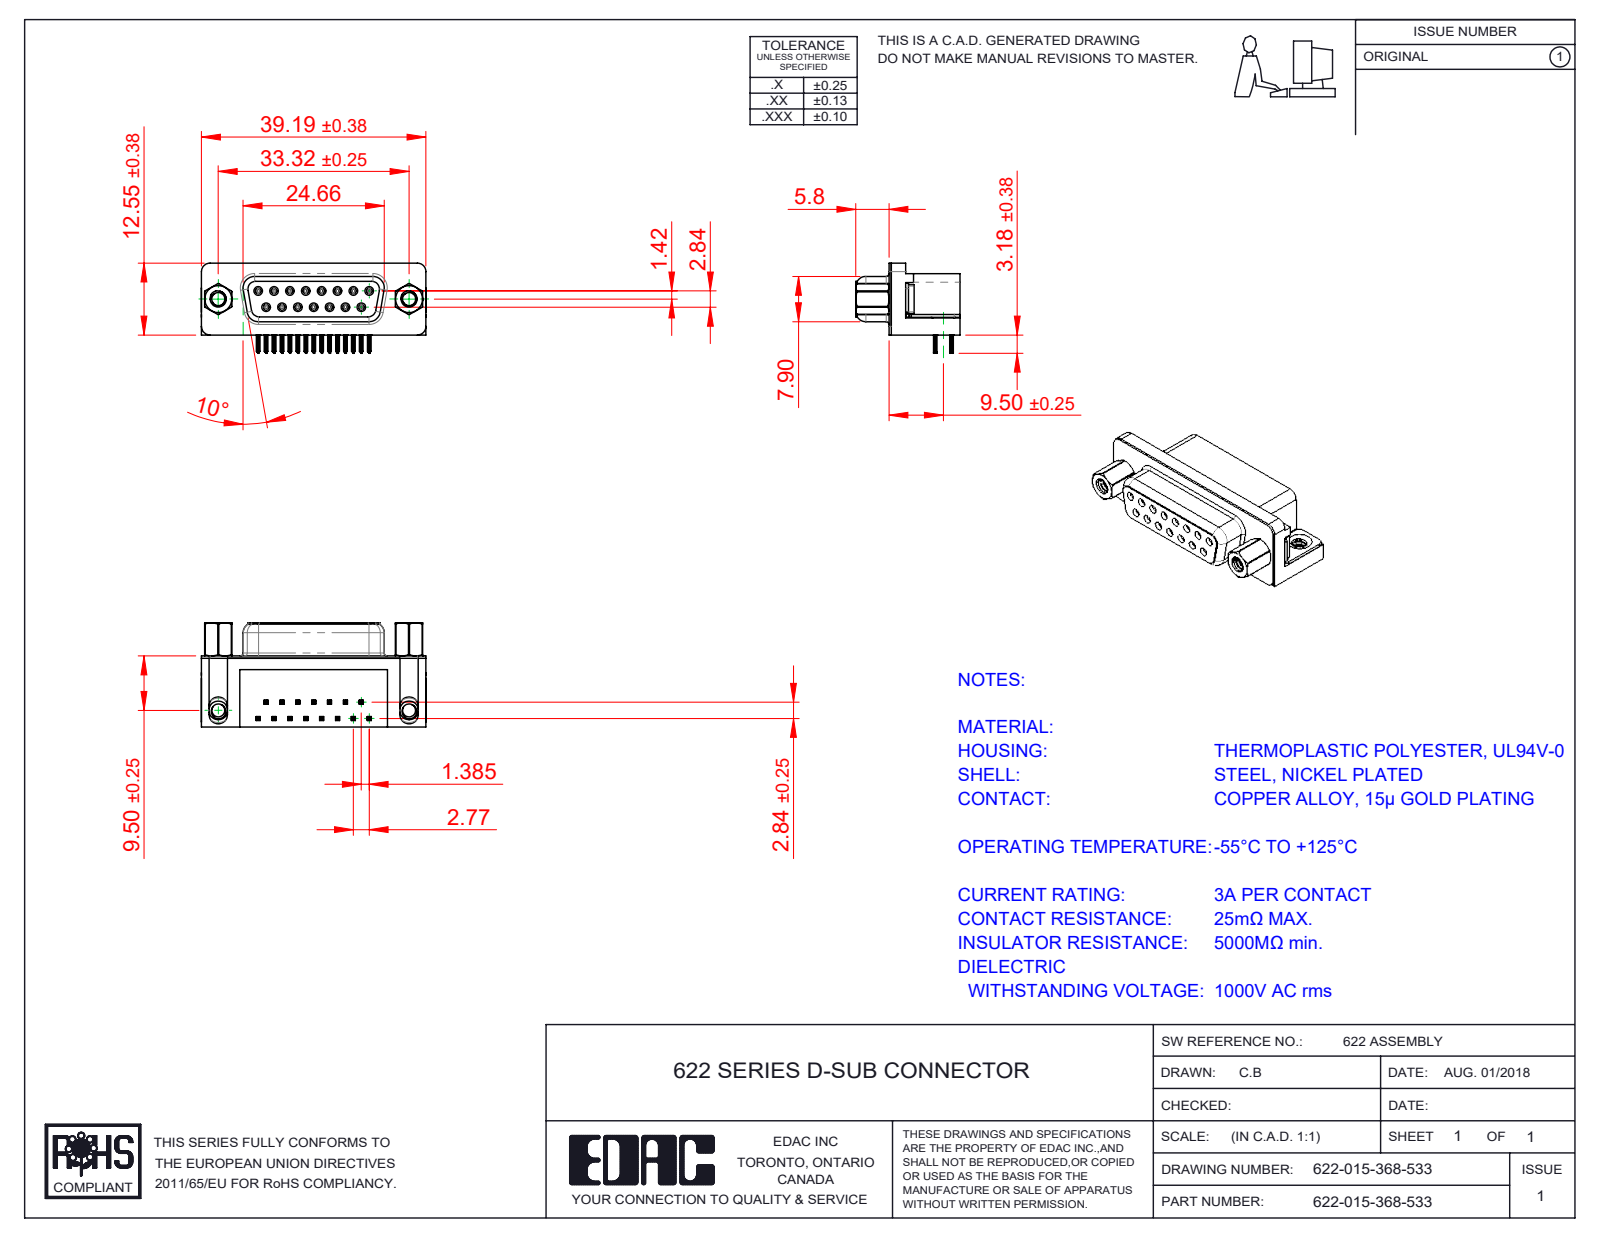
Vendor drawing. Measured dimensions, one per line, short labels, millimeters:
name: 622 2 Prong Board Lock; 622 Shell_15 Socket; 622 Contact Top; 622 4-40 Threaded Rivet (+4 more)
written by: SolidWorks 2016 (CONFIG_CONTROL_DESIGN)
unit: mm
bodies: 23 solids, 2587 faces (1128 planar, 677 cylindrical, 782 other)
size: 39.22 × 18.2 × 16.25
volume: 5 389 mm³; area: 7 174 mm²
holes: 15× ⌀0.8, 15× ⌀0.9, 2× ⌀2.26, 2× ⌀2.29, 2× ⌀4, 2× ⌀4.8, 2× ⌀5
bosses: 15× ⌀1.2, 2× ⌀4.9, 2× ⌀4.75, 2× ⌀3.9, 2× ⌀2.79
rounds: 120× R0.1, 60× R0.15, 30× R0.35, 18× R1, 15× R0.34, 10× R0.5, 8× R0.25, 8× R1.35
face distances: 0.4, 12, 6.2, 12.4, 10.35, 2.9, 0.85, 6.65, 0.35, 5.8
hole spacings: 3.16, 2.77, 5.54, 8.31, 11.08, 5.03, 5.04, 7.48
